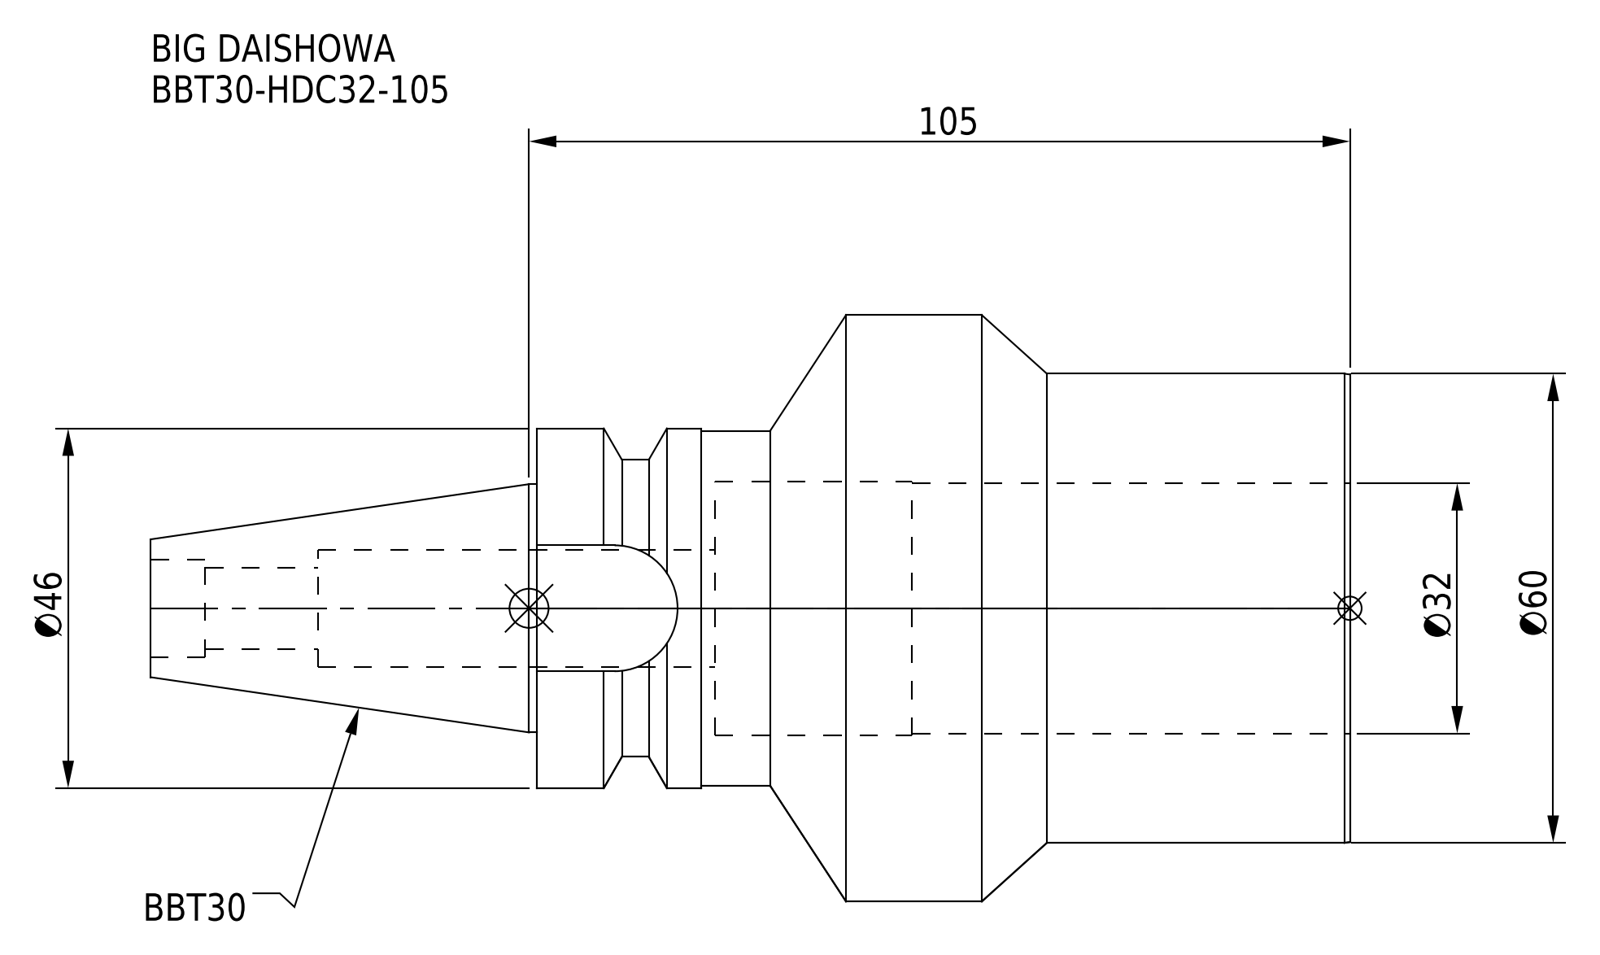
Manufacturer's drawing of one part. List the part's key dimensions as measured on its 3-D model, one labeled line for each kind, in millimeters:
Part name (STEP PRODUCT): BBT30-HDC32-105
STEP written by: CREO PARAMETRIC BY PTC INC, 2016380 (AUTOMOTIVE_DESIGN)
Units: millimetres
Bodies: 1 solid, 54 faces (14 planar, 28 cylindrical, 12 other)
Overall size (bounding box): 153.4 × 75 × 75
Volume: 235 551 mm³ · Surface area: 41 028 mm²
Round holes (diameter × count): ⌀10.4 ×1, ⌀12.5 ×1, ⌀15 ×1, ⌀32 ×1, ⌀32.5 ×1
Round bosses / shafts (diameter × count): ⌀75 ×1, ⌀60 ×1, ⌀46 ×1, ⌀45.4 ×1, ⌀31.75 ×1
Partial cylindrical surfaces — rounded edges, fillets, slot ends (radius × count): R8.05 ×1, R19 ×1
Main face-to-face distances: 104, 81.2, 22.8, 32.6, 153.4, 72.2, 49.4, 16.1, 132, 50.8
